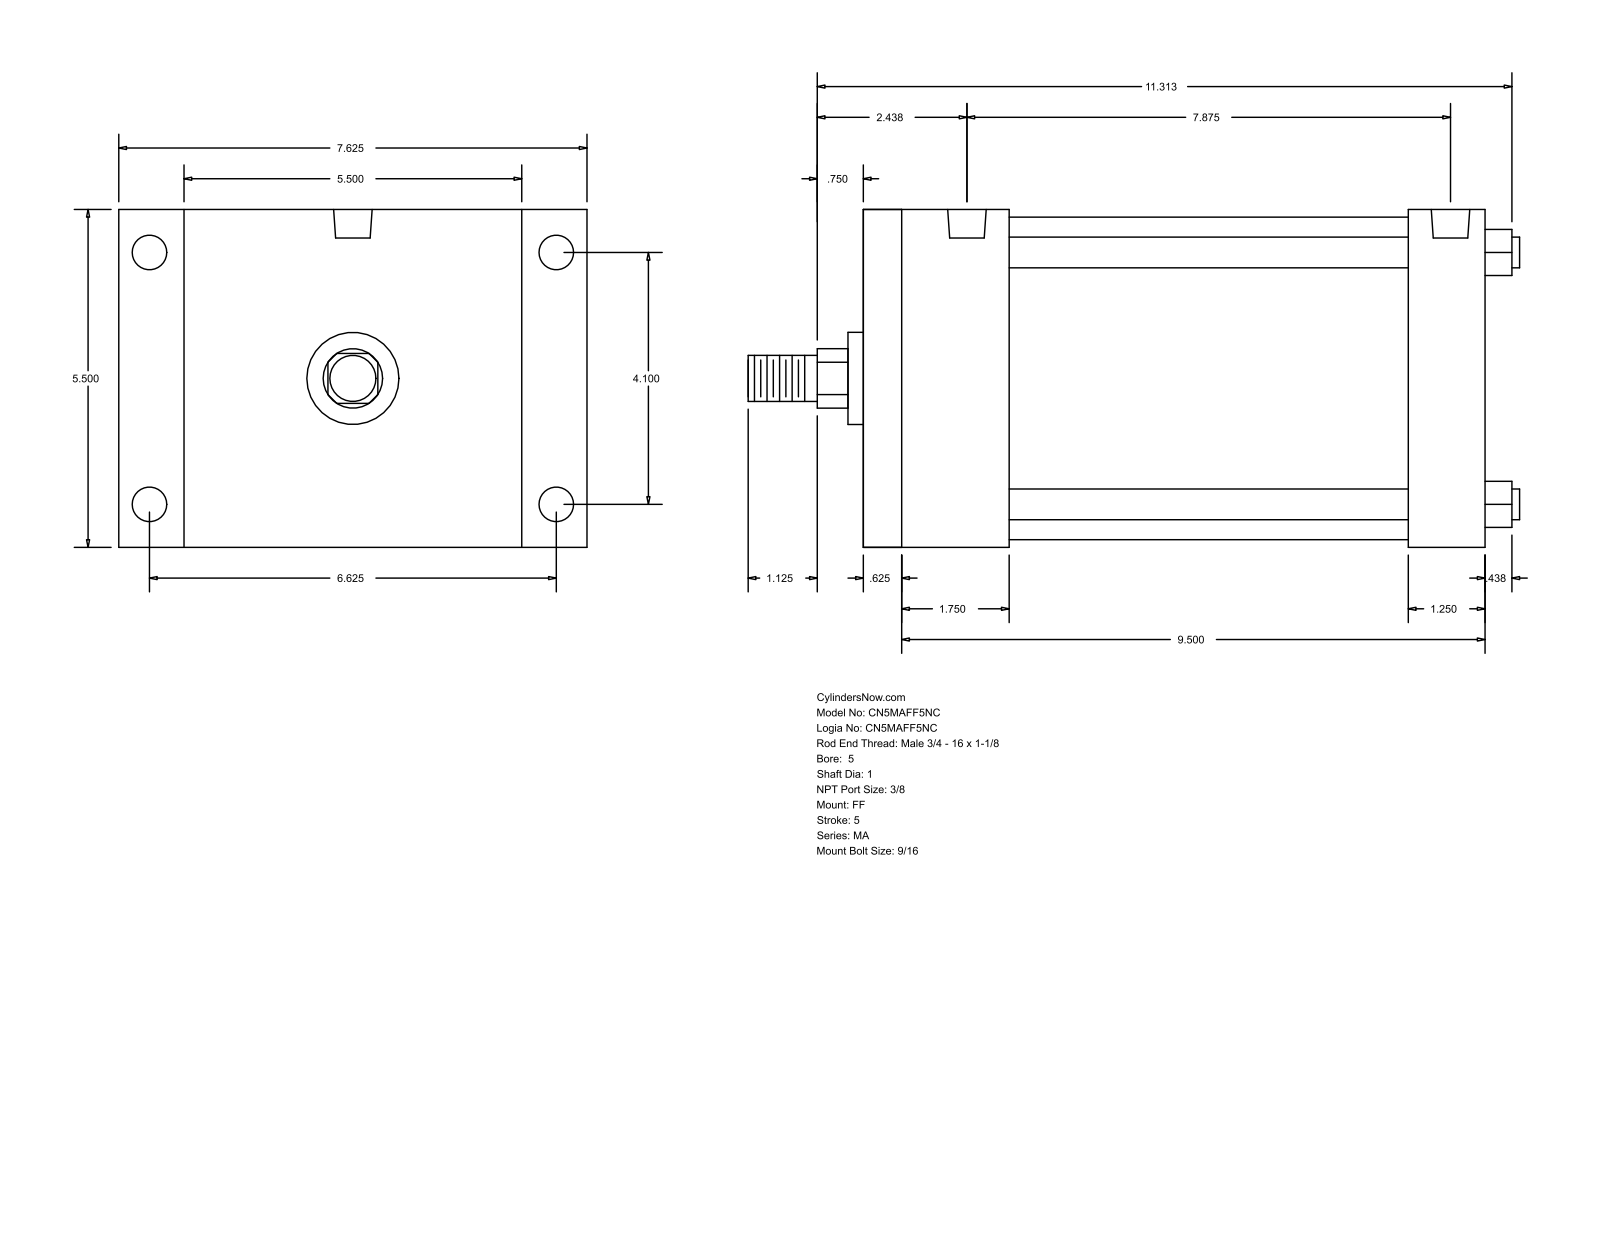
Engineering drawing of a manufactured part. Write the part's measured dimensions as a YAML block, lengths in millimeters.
part_name: "MA_FF__0500_1"
step_written_by: "GSSL Pune (CONFIG_CONTROL_DESIGN)"
units: millimeters
bodies: {solids: 0, faces: 92, planar: 64, cylindrical: 28, other: 0}
overall_size: [319.09, 193.68, 139.7]
round_holes:
  - {diameter: 11.11, count: 4}
  - {diameter: 14.29, count: 4}
  - {diameter: 15.93, count: 2}
round_bosses_or_shafts:
  - {diameter: 12.7, count: 4}
  - {diameter: 133.35, count: 1}
  - {diameter: 38.1, count: 1}
  - {diameter: 25.4, count: 1}
  - {diameter: 19.05, count: 1}
partial_cylinders:
  - {radius: 12.29, count: 1}
face_to_face_distances: [139.7, 257.18, 15.87, 241.31, 225.42, 209.55, 31.76, 60.33, 44.46, 165.09]
hole_center_spacings: [4.76, 104.14, 168.28, 190.51, 195.27, 197.9, 200.03]
